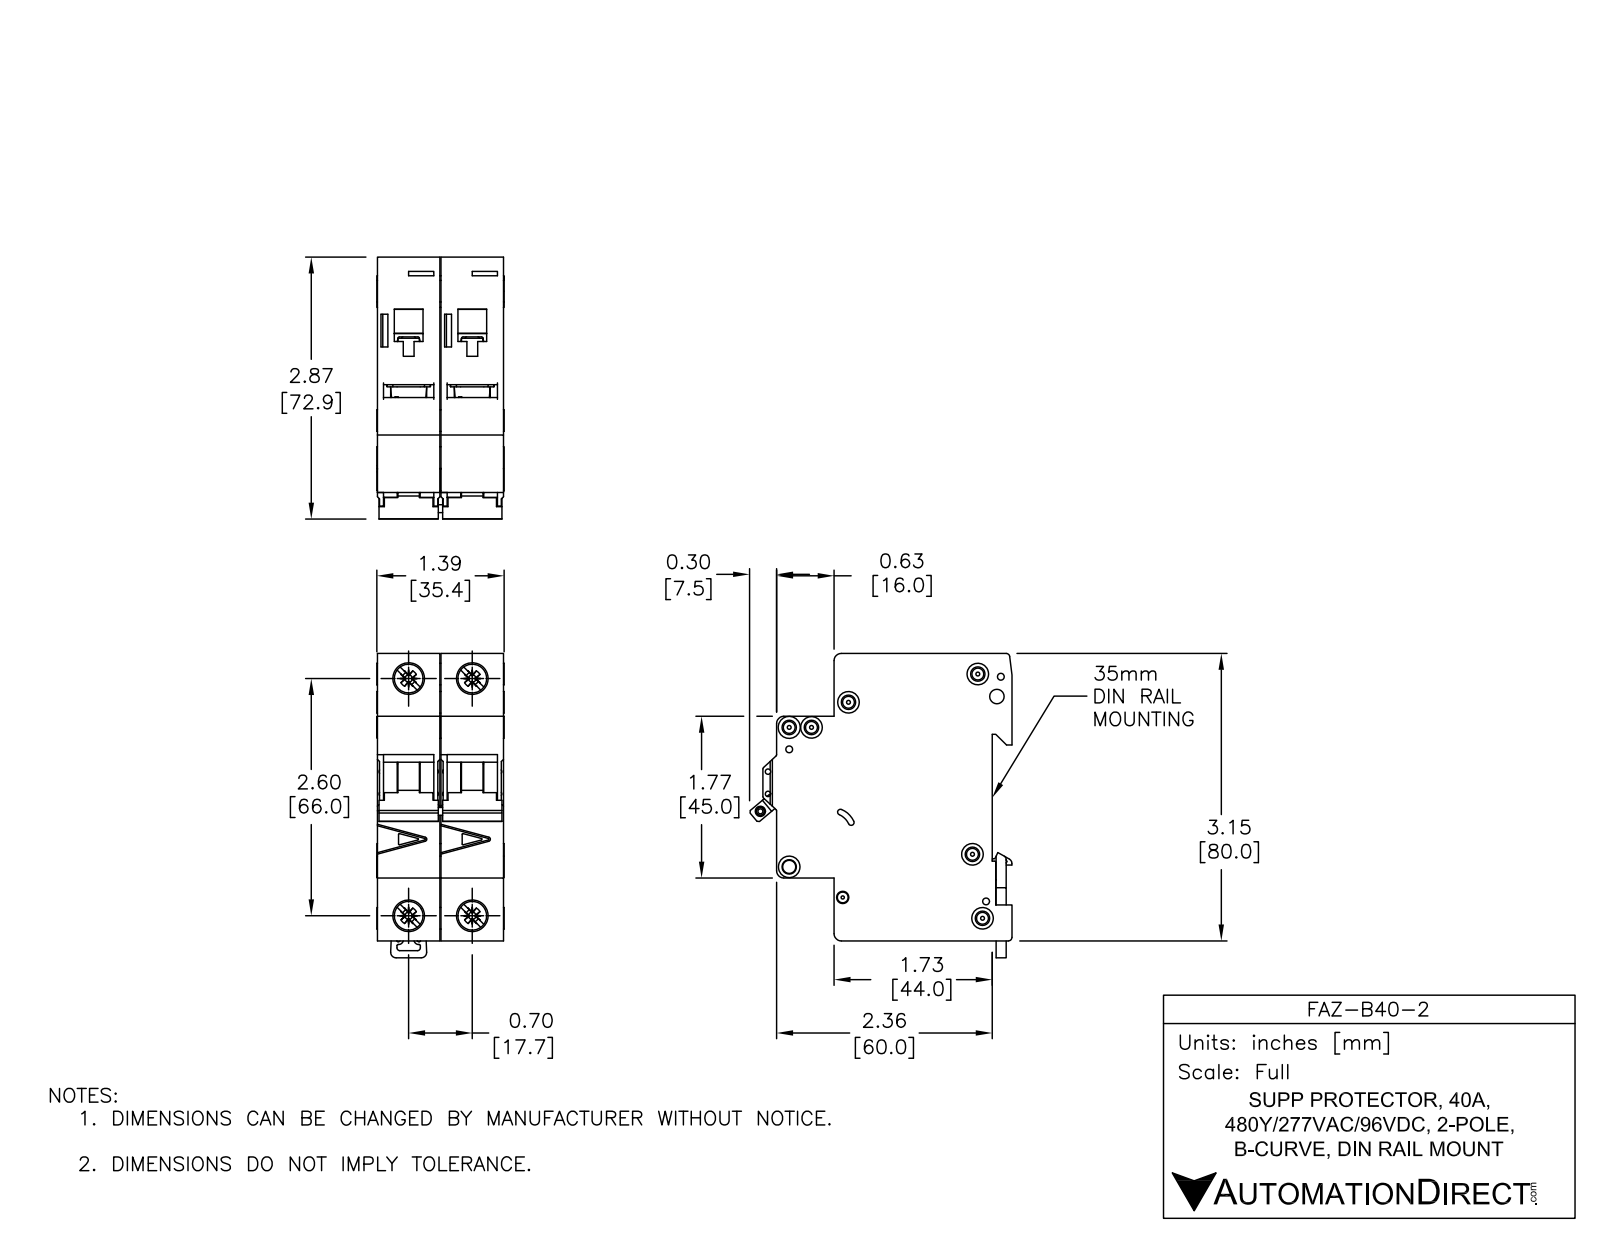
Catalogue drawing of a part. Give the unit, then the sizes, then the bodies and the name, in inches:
Units: inches
Overall size (bounding box): 3.338 × 2.876 × 1.394
Round holes (diameter × count): ⌀0.142 ×6, ⌀0.075 ×3, ⌀0.043 ×2, ⌀0.059 ×2, ⌀0.157 ×2, ⌀0.281 ×2, ⌀0.323 ×2, ⌀0.085 ×1, ⌀0.087 ×1, ⌀0.1 ×1, ⌀0.13 ×1, ⌀0.134 ×1
Round bosses / shafts (diameter × count): ⌀0.236 ×4, ⌀0.323 ×2, ⌀0.098 ×2
Partial cylindrical surfaces — rounded edges, fillets, slot ends (radius × count): R0.01 ×49, R0.02 ×19, R0.079 ×10, R0.008 ×8, R0.039 ×8, R0.031 ×2, R0.071 ×2, R0.118 ×2
Main face-to-face distances: 0.697, 0.689, 1.386, 3.129, 0.217, 1.949, 1.732, 2.579, 2.362, 0.63
Hole centre spacings: 0.244, 0.537, 0.697, 2.598, 2.69, 0.189, 0.204, 0.221
Volume: 9.142 in³ · Surface area: 60.14 in²
Bodies: 8 solids, 1104 faces (466 planar, 396 cylindrical, 242 other)
Part name (STEP PRODUCT): FAZ-B40-2
STEP written by: SolidWorks 2014 (AUTOMOTIVE_DESIGN)
